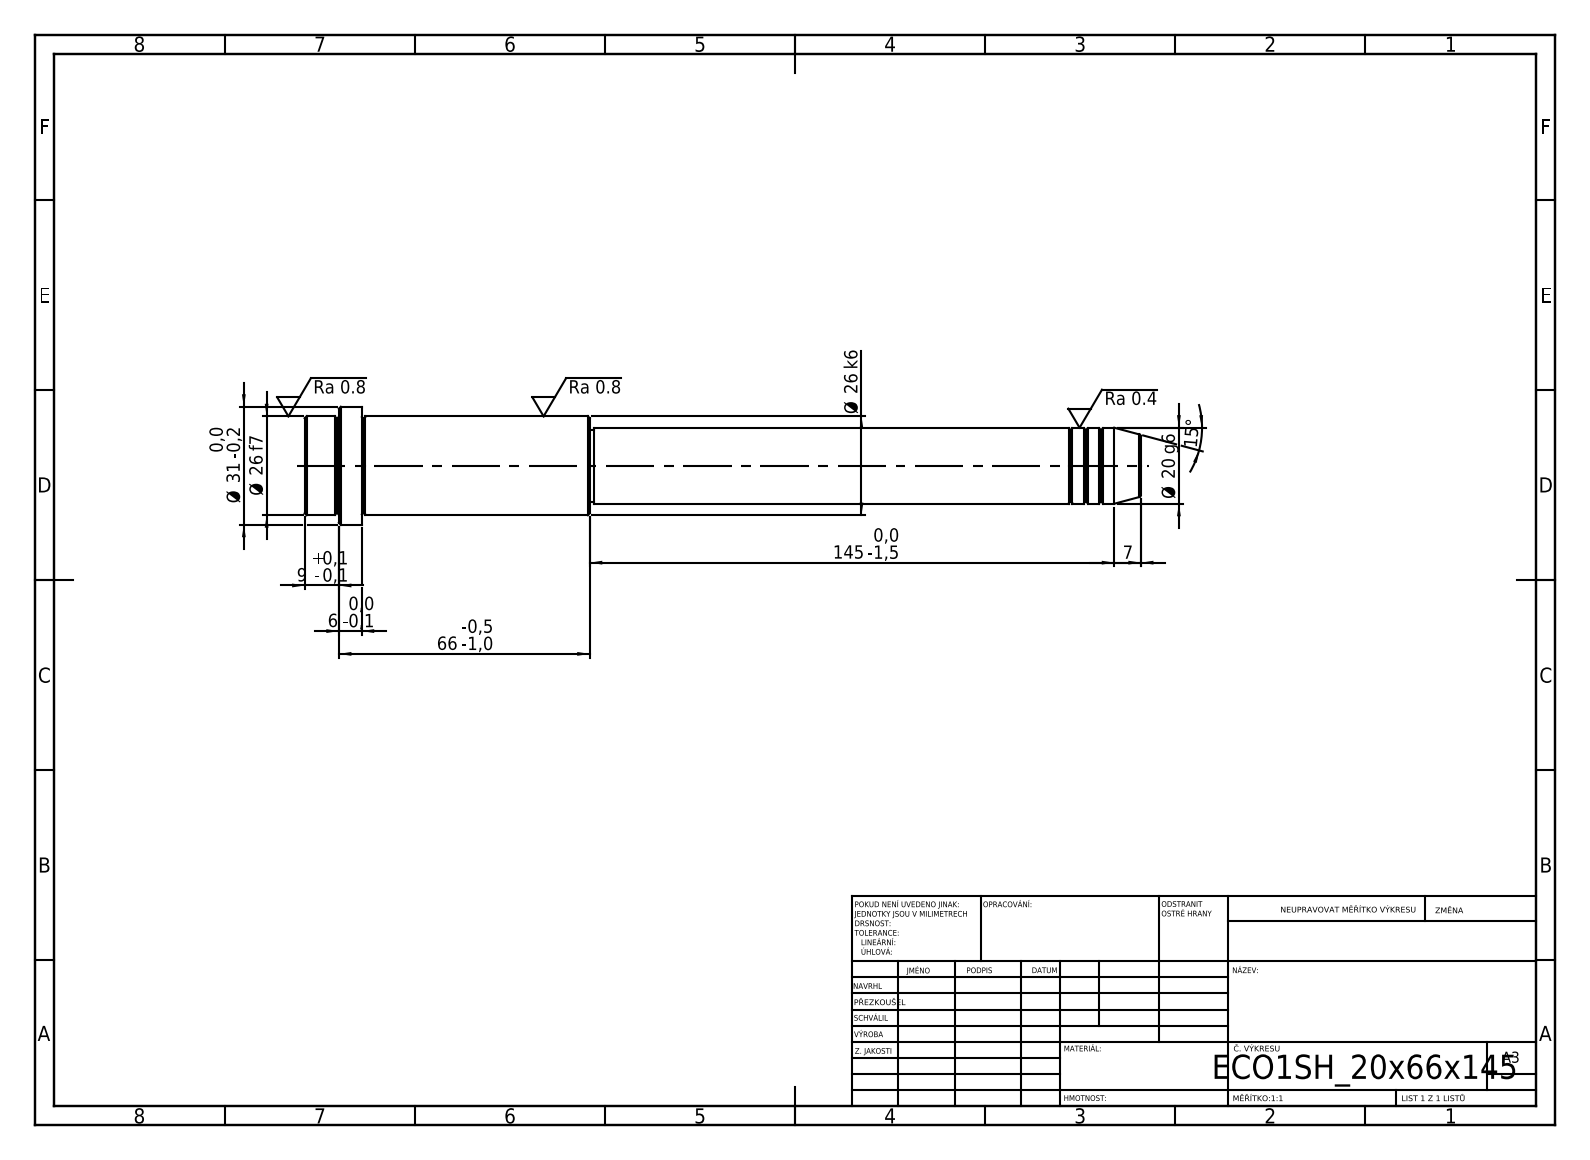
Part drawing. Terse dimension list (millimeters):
written by: SolidWorks 2019 (CONFIG_CONTROL_DESIGN)
unit: mm
bodies: 1 solid, 52 faces (6 planar, 16 cylindrical, 30 other)
size: 220 × 31 × 31
volume: 86 129 mm³; area: 16 867 mm²
bosses: 1× ⌀31, 1× ⌀26, 1× ⌀20, 1× ⌀19
face distances: 15, 60, 75, 145, 205, 220, 211, 66, 6, 9
